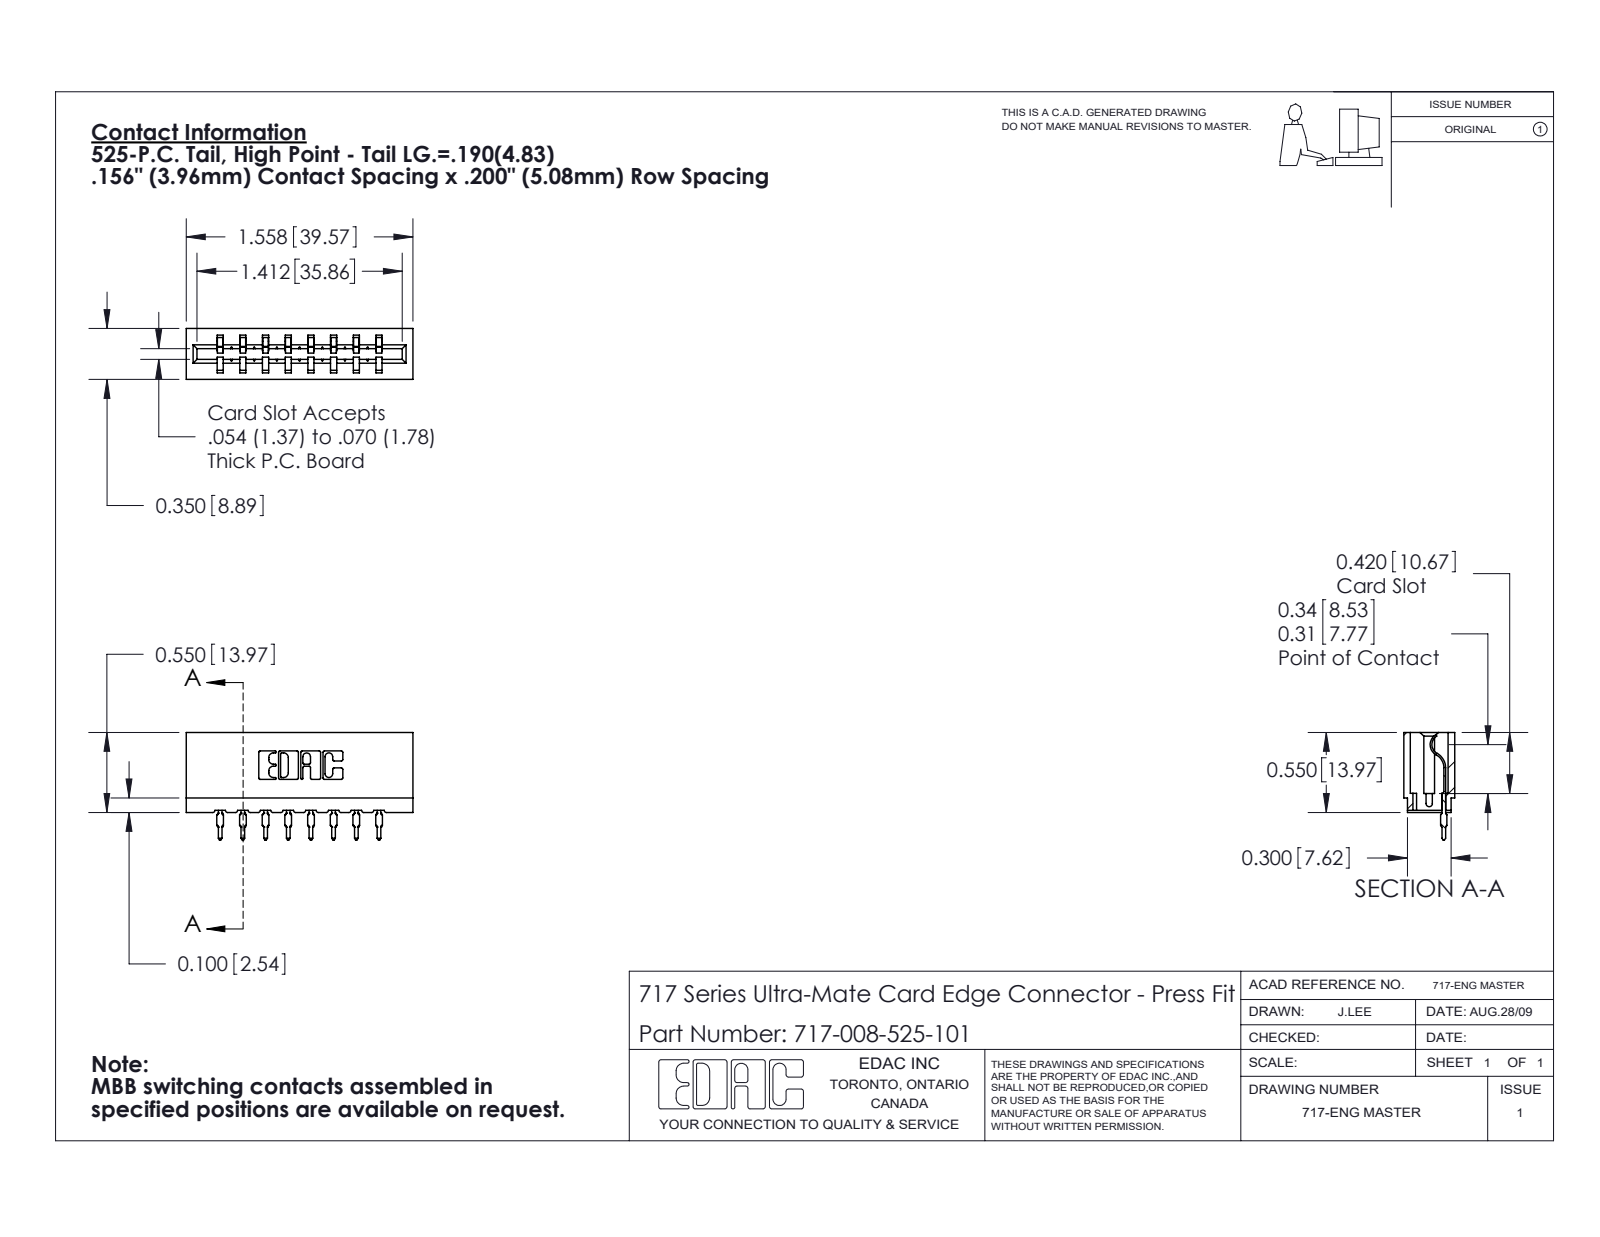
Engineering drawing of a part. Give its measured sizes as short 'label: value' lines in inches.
name: 717-008-525-101; 745-292-001_525; 717 Part_Insulator Option - 06
written by: SolidWorks 2020 (CONFIG_CONTROL_DESIGN)
unit: in
bodies: 9 solids, 998 faces (598 planar, 192 cylindrical, 208 other)
size: 1.558 × 0.739 × 0.35
volume: 0.213 in³; area: 6.986 in²
rounds: 22× R0.01, 16× R0.015, 16× R0.021, 6× R0.007, 6× R0.031, 4× R0.005, 4× R0.011, 3× R0.026
face distances: 0.212, 0.156, 0.138, 0.624, 0.468, 0.198, 0.312, 0.35, 0.042, 0.27
